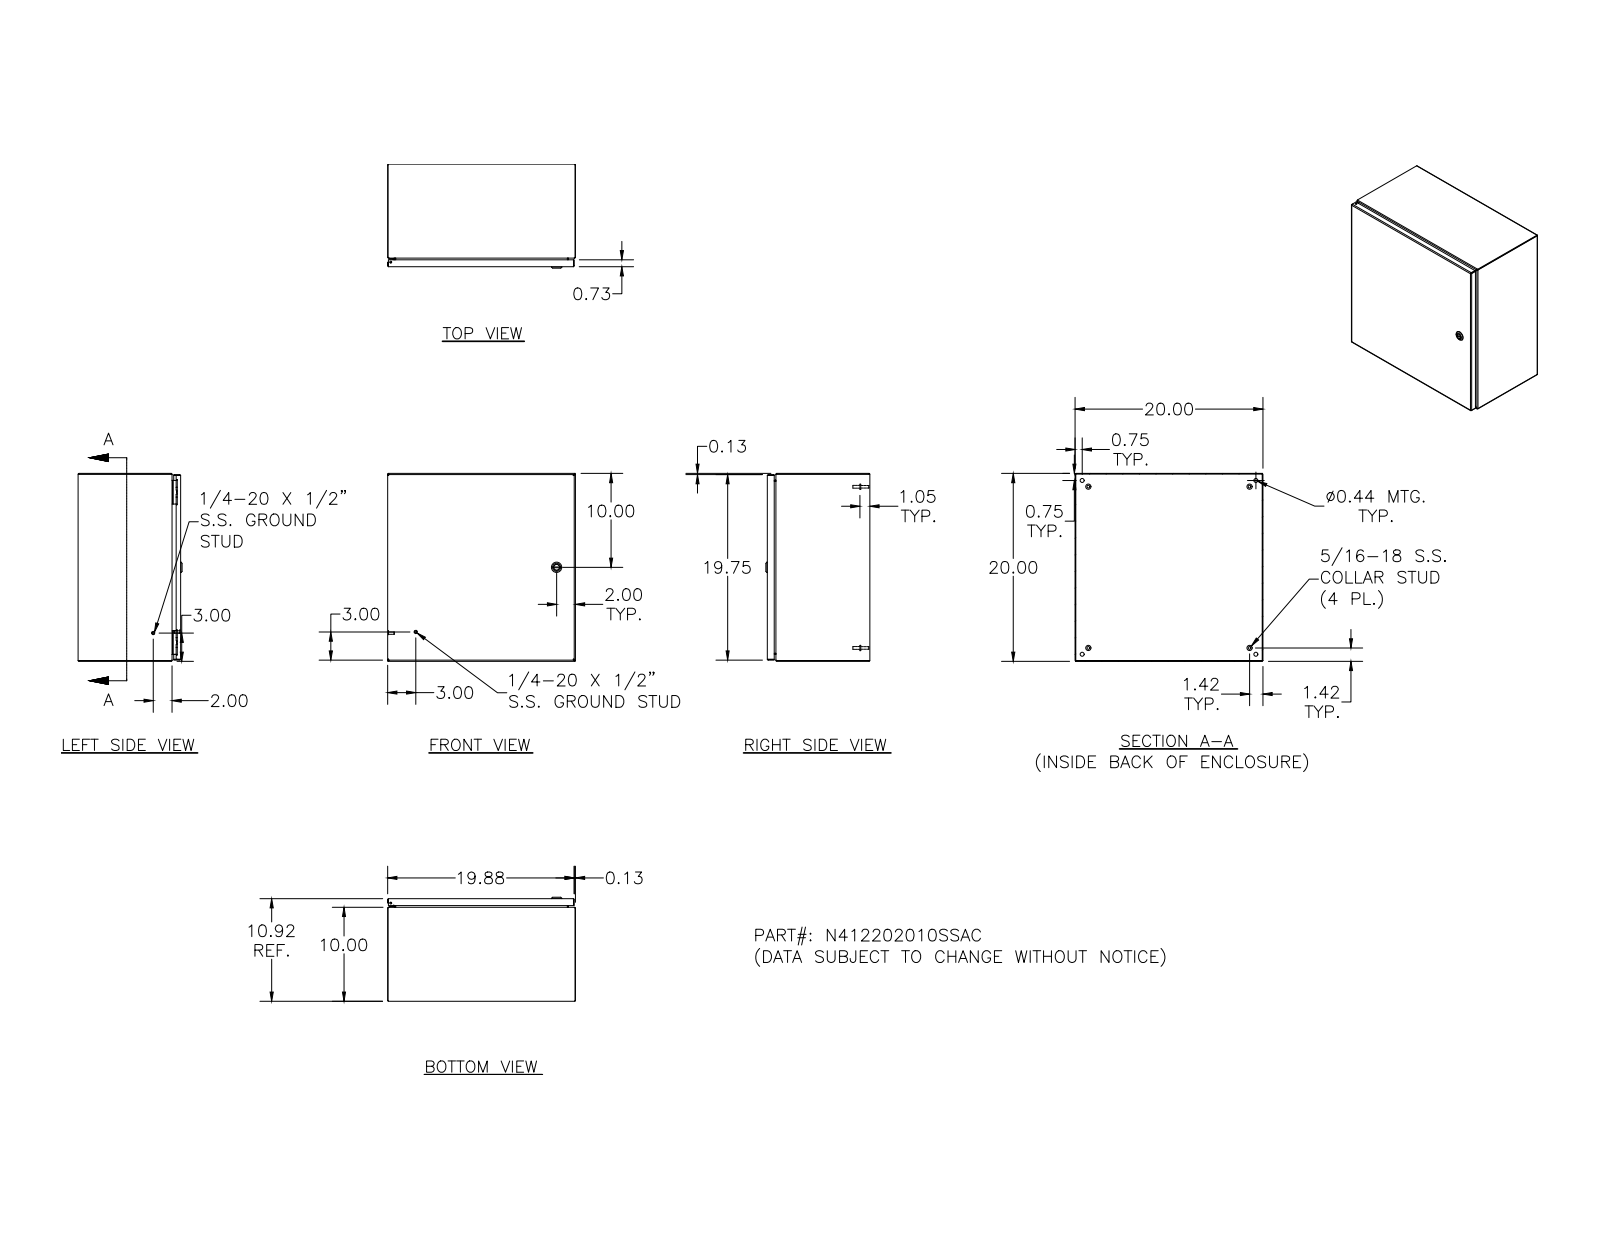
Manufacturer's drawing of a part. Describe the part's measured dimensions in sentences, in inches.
The part is named "N412202010SSAC; N412202010SSACBKP; 388151; N4122020SSACLID (+8 more)". Its 3-D file was written by "Autodesk Inventor 2011 (AUTOMOTIVE_DESIGN)". It is 34 solids with 1364 faces: 523 planar, 497 cylindrical and 344 other. Overall it measures 20 by 20 by 11.075 inches. Its volume is 130.5 cubic inches and its surface area 3 547 square inches. Round holes: 5 of diameter 0.188, 4 of diameter 0.093, 4 of diameter 0.152, 4 of diameter 0.167, 4 of diameter 0.172, 4 of diameter 0.437, 2 of diameter 0.156, 1 of diameter 0.187, 1 of diameter 0.197, 1 of diameter 0.315, 1 of diameter 0.394, 1 of diameter 0.402. Round bosses or shafts: 10 of diameter 0.25, 4 of diameter 0.563, 4 of diameter 0.36, 4 of diameter 0.32, 4 of diameter 0.3, 4 of diameter 0.275, 4 of diameter 0.256, 4 of diameter 0.164. Partial cylindrical surfaces (rounded edges, fillets, slot ends): 26 of radius 0.05, 18 of radius 0.016, 16 of radius 0.016, 16 of radius 0.09, 14 of radius 0.031, 14 of radius 0.125, 9 of radius 0.02, 8 of radius 0.032. The main face-to-face distances are 0.074, 19.926, 10.843, 19.852, 20, 10.769, 10.917, 9.926, 0.917, 19.187. The hole center spacings are 16, 0.017, 0.66, 16.008, 18.5, 18.872, 0.019, 0.5.
